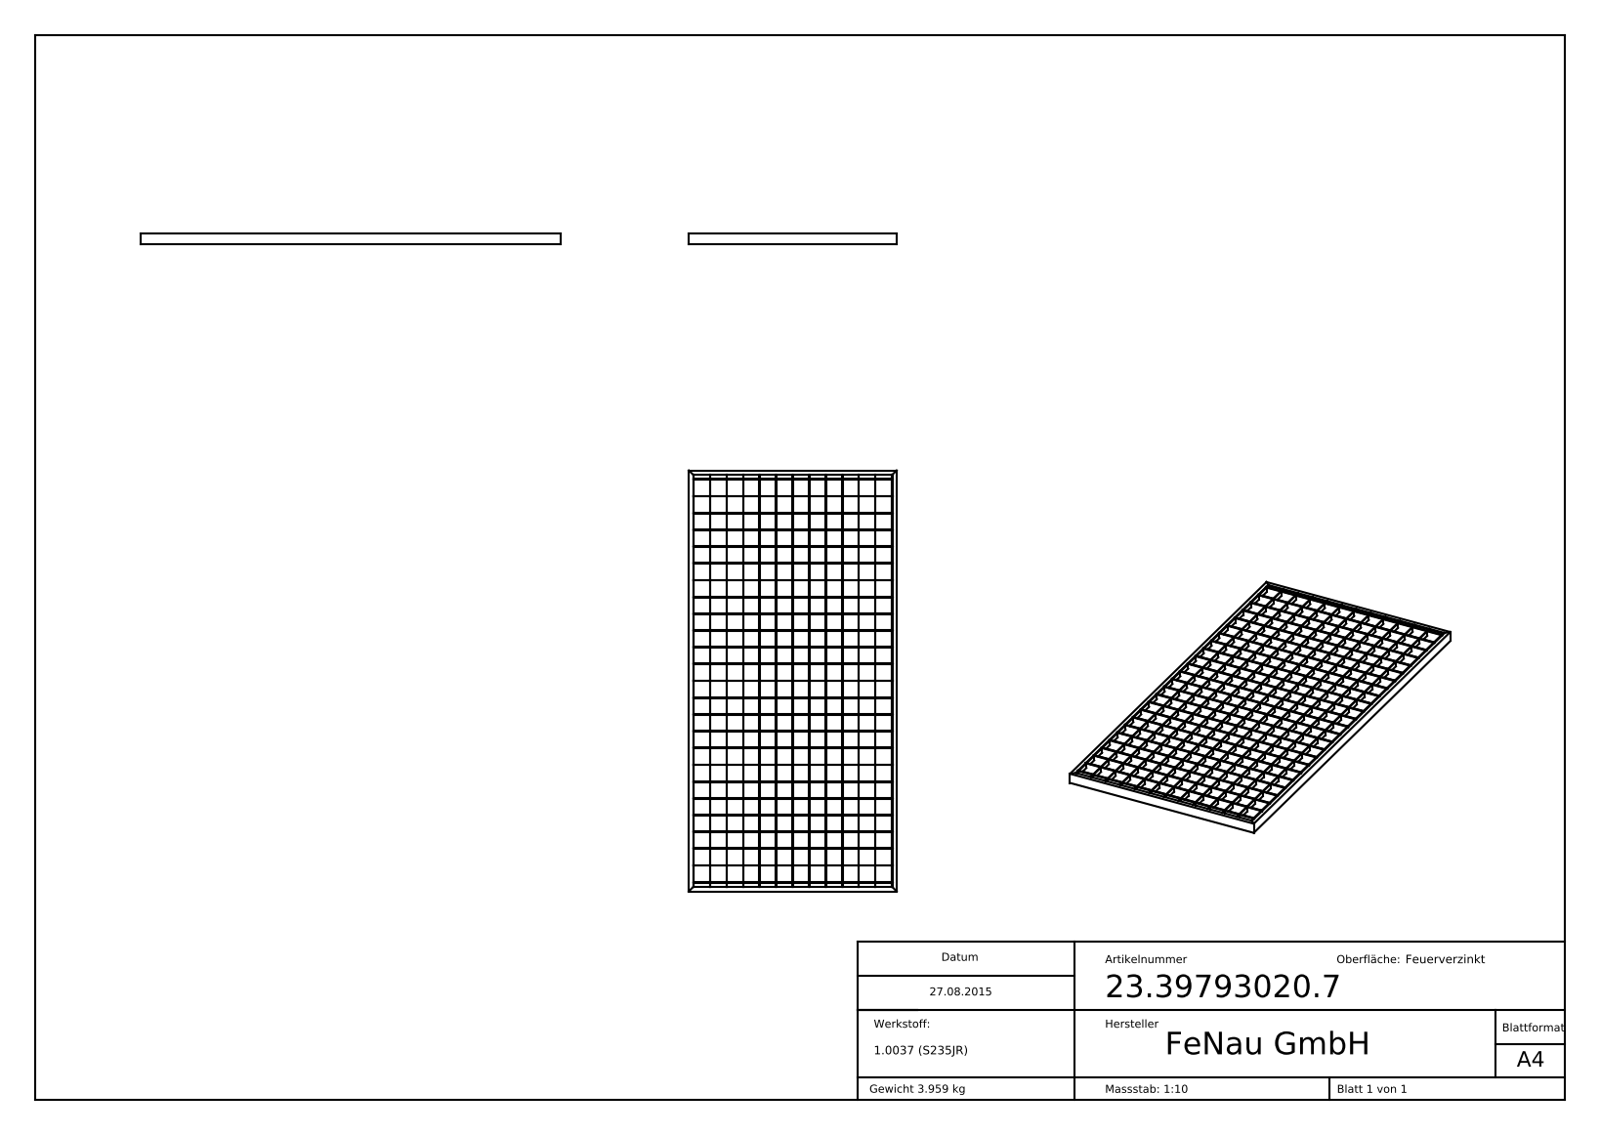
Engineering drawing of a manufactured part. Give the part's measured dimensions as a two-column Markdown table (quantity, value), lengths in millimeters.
| quantity | value |
| --- | --- |
| part name | 23-39793020-7 |
| STEP written by | SolidWorks 2015 (CONFIG_CONTROL_DESIGN) |
| units | millimeters |
| bodies | 1 solid, 1286 faces (1286 planar, 0 cylindrical, 0 other) |
| overall size | 790 × 390 × 20 |
| volume | 507 513 mm³ |
| surface area | 748 957 mm² |
| main face-to-face distances | 63, 31.5, 94.5, 126, 157.5, 31, 189, 220.5, 252, 62 |
